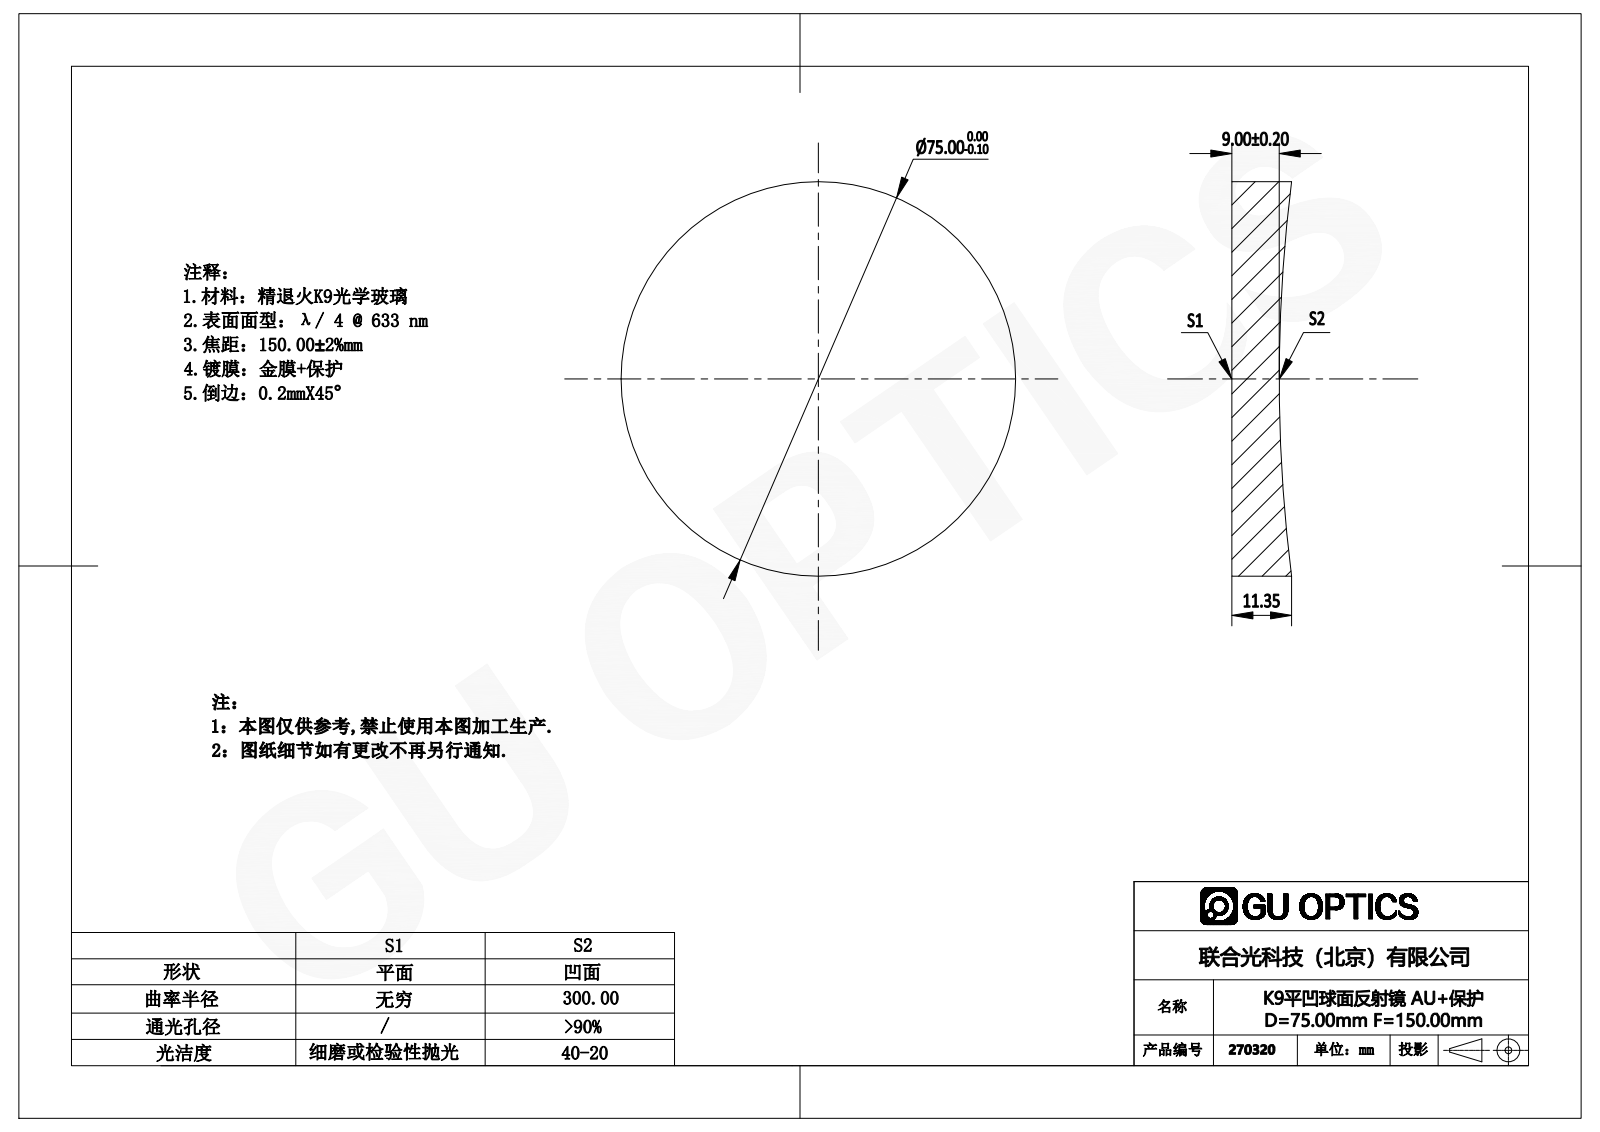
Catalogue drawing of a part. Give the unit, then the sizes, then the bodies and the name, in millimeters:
Units: millimetres
Overall size (bounding box): 75 × 75 × 11.35
Round bosses / shafts (diameter × count): ⌀75 ×1
Volume: 44 952 mm³ · Surface area: 11 528 mm²
Bodies: 1 solid, 5 faces (1 planar, 2 cylindrical, 2 other)
Part name (STEP PRODUCT): 270060
STEP written by: SolidWorks 2016 (AUTOMOTIVE_DESIGN)
